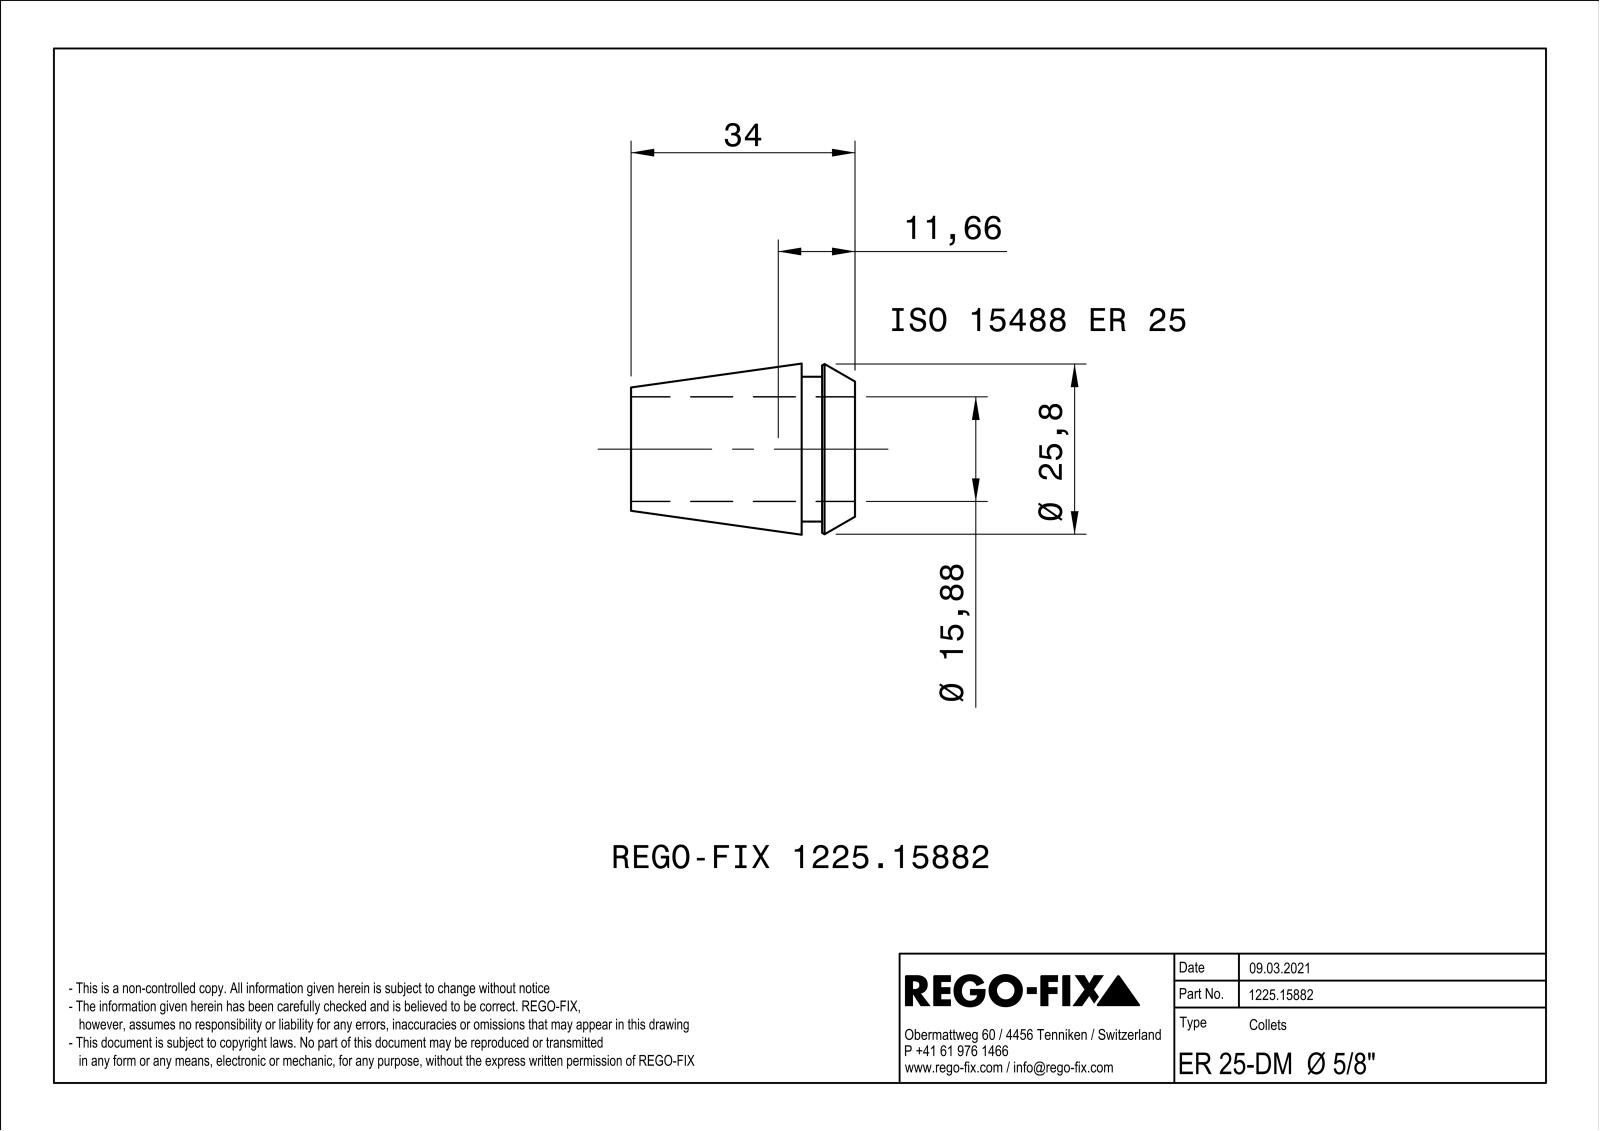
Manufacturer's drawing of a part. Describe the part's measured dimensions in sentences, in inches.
The part is named "NOCUT". Its 3-D file was written by "SIEMENS PLM Software Solid Edge ST10 (AUTOMOTIVE_DESIGN)". It is 1 solid with 154 faces: 80 planar, 9 cylindrical and 65 other. Overall it measures 1.339 by 1.023 by 1.023 inches. Its volume is 0.358 cubic inches and its surface area 10.07 square inches. Round holes: 1 of diameter 0.625. Round bosses or shafts: 1 of diameter 0.866. The main face-to-face distances are 0.031, 0.197, 0.122, 0.319, 1.142, 1.339, 1.02, 0.591, 0.394, 0.272.
